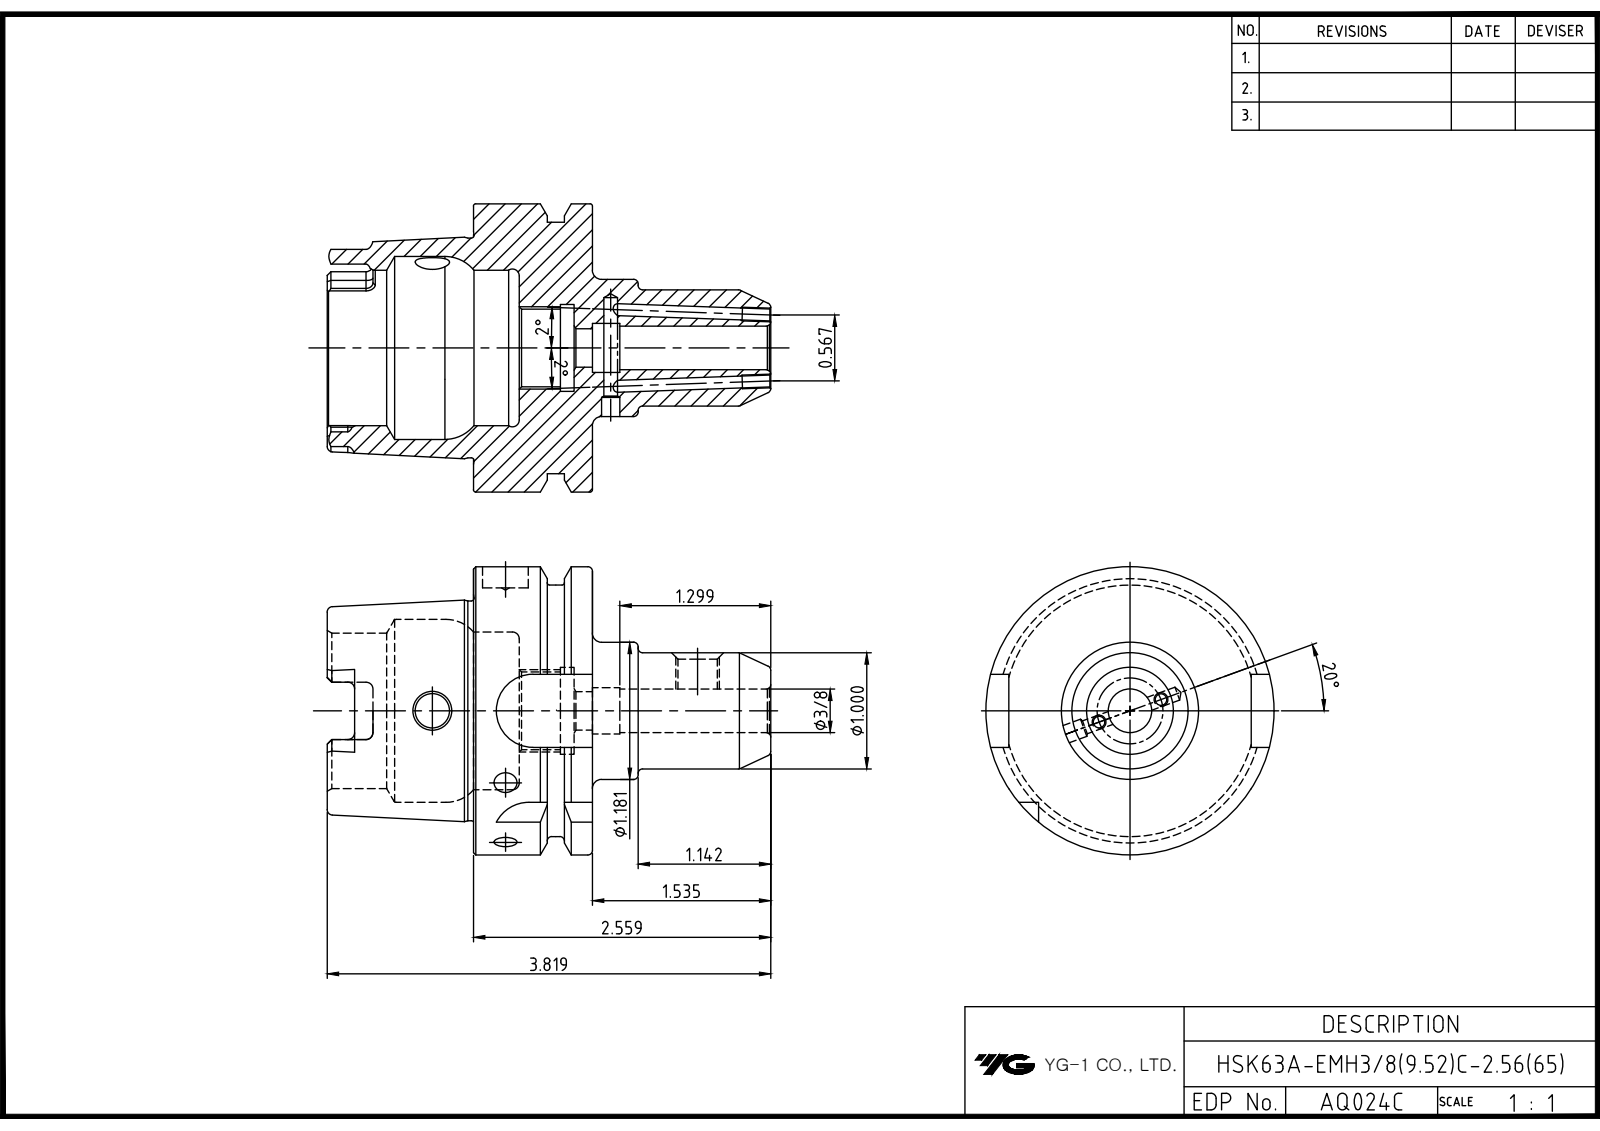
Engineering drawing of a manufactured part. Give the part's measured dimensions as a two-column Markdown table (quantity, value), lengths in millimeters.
| quantity | value |
| --- | --- |
| part name | LO-HSK63A-EMH9.525C-65 |
| STEP written by | Autodesk Inventor 2022 (AUTOMOTIVE_DESIGN) |
| units | millimeters |
| bodies | 1 solid, 125 faces (43 planar, 37 cylindrical, 45 other) |
| overall size | 97 × 63 × 63 |
| volume | 98 809 mm³ |
| surface area | 26 956 mm² |
| round holes (diameter × count) | 2.46 × 2, 7.5 × 1, 8.38 × 1, 8.4 × 1, 9.52 × 1, 10 × 1, 10.72 × 1, 16.92 × 1, 19 × 1, 34 × 1, 40 × 1 |
| round bosses / shafts (diameter × count) | 63 × 1, 55 × 1, 48.04 × 1, 30 × 1, 25.4 × 1 |
| partial cylindrical surfaces (radius × count) | 1.5 × 6, 2.9 × 4, 8 × 4 |
| main face-to-face distances | 26, 10, 16, 32, 58, 42, 53, 22, 4, 12 |
| hole center spacings | 42 |
